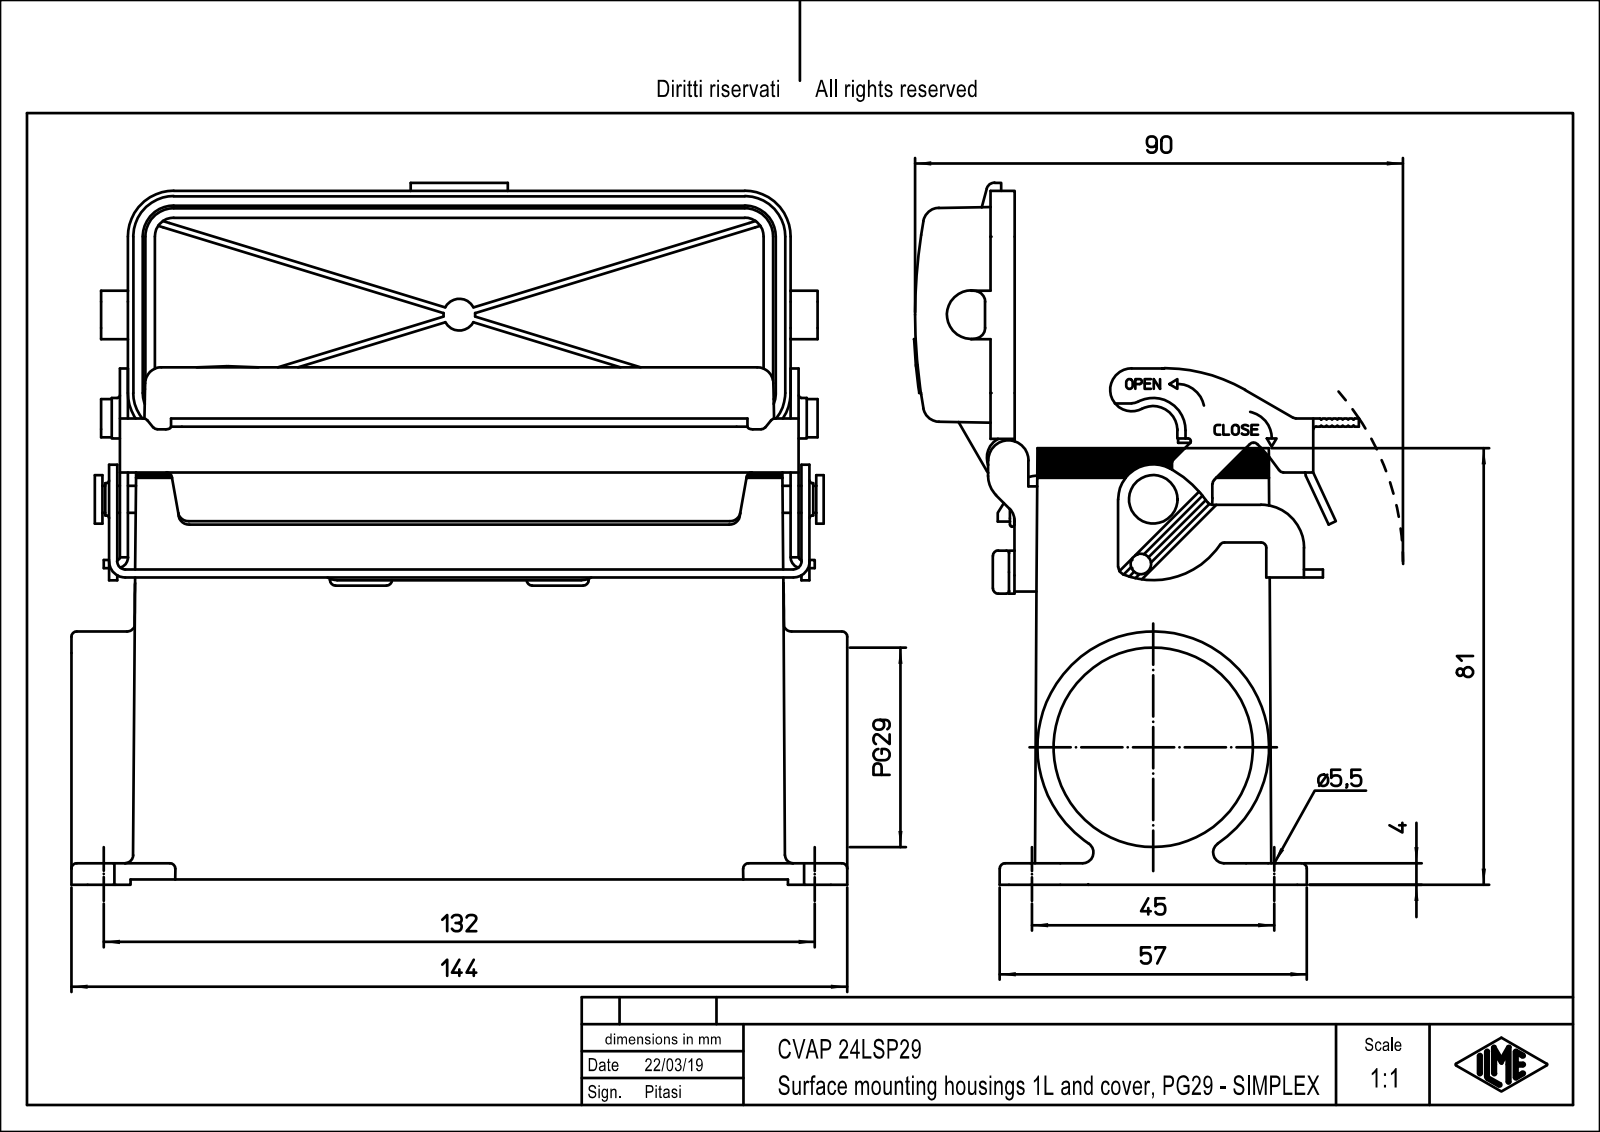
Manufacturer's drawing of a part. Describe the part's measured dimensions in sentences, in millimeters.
The part is named "CVAP_24LSP29". Its 3-D file was written by "PTC Creo Elements/Direct Modeling 19.0E 27-Jun-2016 (C) Parametric Technology GmbH (AUTOMOTIVE_DESIGN)". It is 1 solid with 612 faces: 379 planar, 209 cylindrical and 24 other. Overall it measures 144 by 129.72 by 79.7 millimeters. Its volume is 177 217 cubic millimeters and its surface area 105 632 square millimeters. Round holes: 4 of diameter 2.46, 4 of diameter 3, 4 of diameter 5.5, 1 of diameter 32, 1 of diameter 37. Round bosses or shafts: 3 of diameter 0.8, 1 of diameter 44.5, 1 of diameter 9, 1 of diameter 8.4, 1 of diameter 8, 1 of diameter 6, 1 of diameter 5, 1 of diameter 2.4. Partial cylindrical surfaces (rounded edges, fillets, slot ends): 22 of radius 2, 13 of radius 3, 8 of radius 1.5, 7 of radius 3.5, 5 of radius 1, 5 of radius 6, 4 of radius 0.5, 4 of radius 1.8. The main face-to-face distances are 4, 40.5, 44.5, 36.5, 1.5, 11.75, 120.5, 2, 40.3, 3.5. The hole center spacings are 16.64, 38.63, 118.34, 123.37, 27, 45, 104, 107.45.
